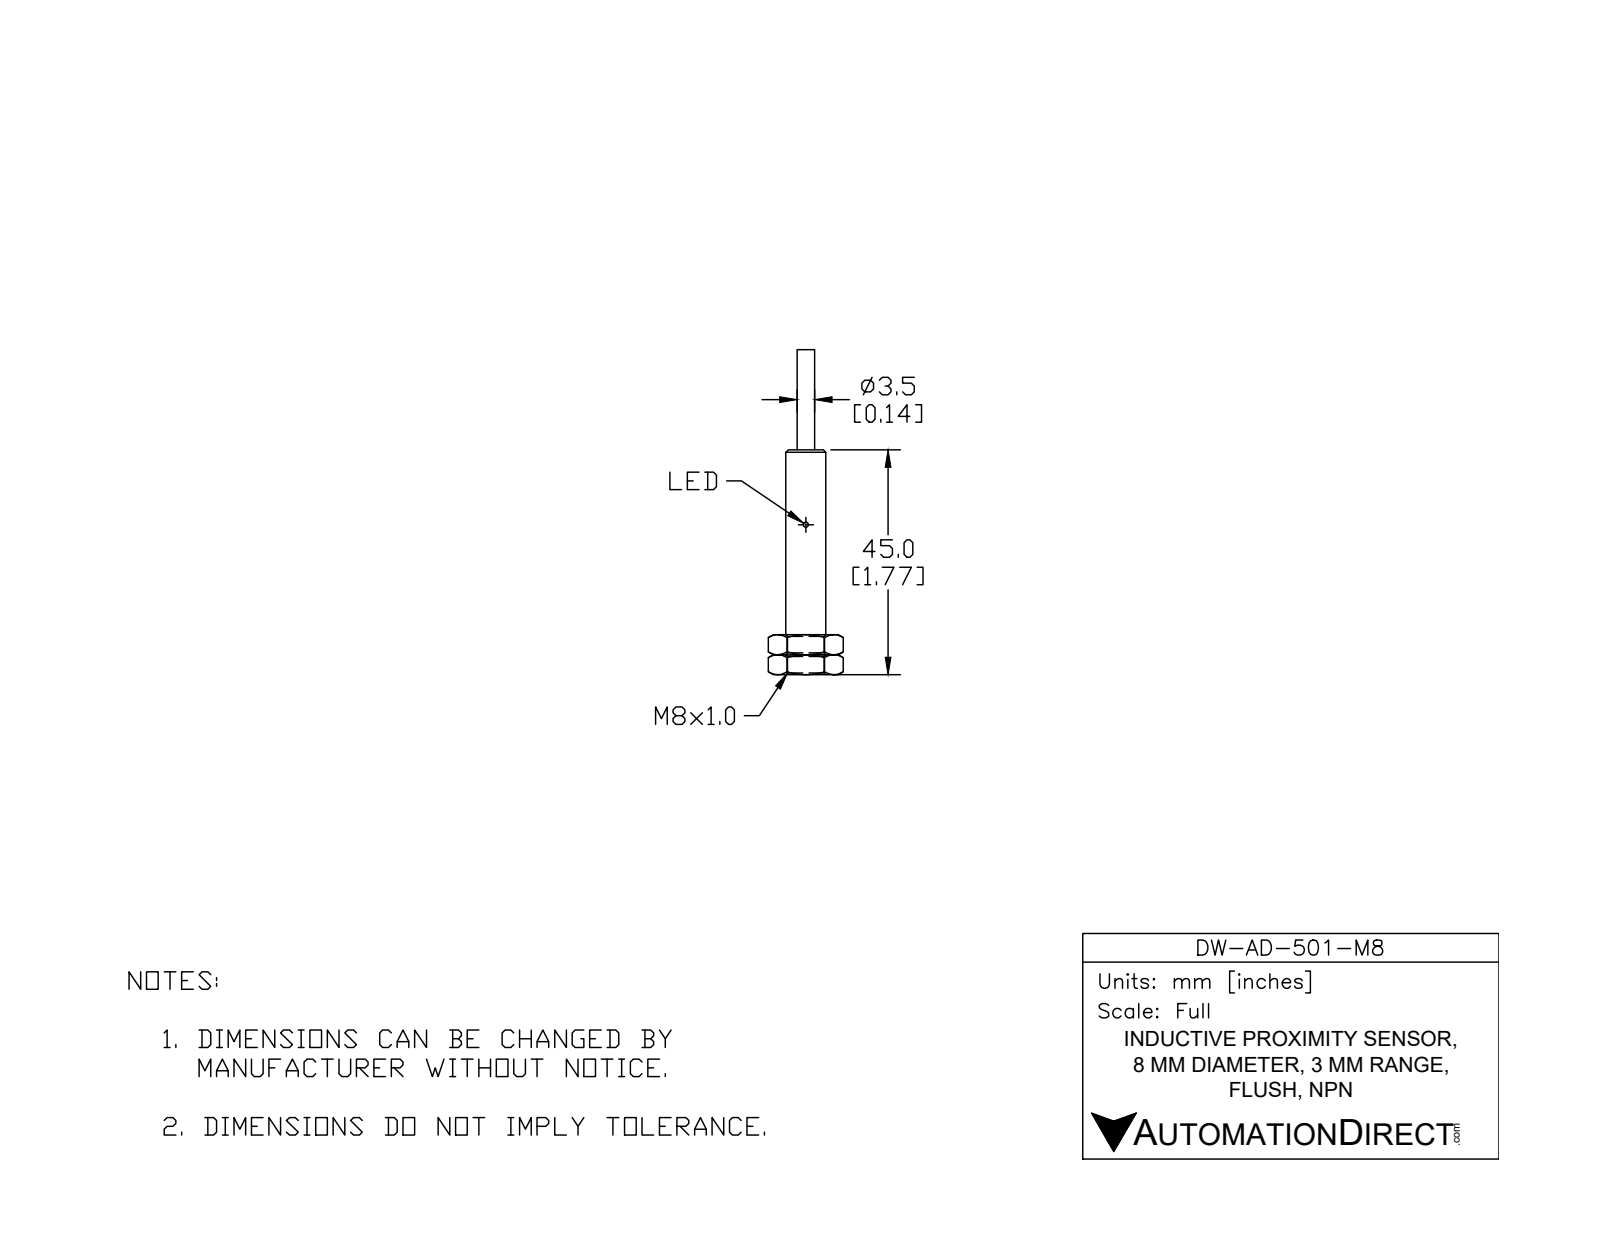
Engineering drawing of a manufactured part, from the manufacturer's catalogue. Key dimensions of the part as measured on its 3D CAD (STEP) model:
Part name (STEP PRODUCT): DW-AD-501-M8
STEP written by: SolidWorks 2017 (AUTOMOTIVE_DESIGN)
Units: inches
Bodies: 1 solid, 10 faces (4 planar, 3 cylindrical, 3 other)
Overall size (bounding box): 2.803 × 0.315 × 0.315
Volume: 0.17 in³ · Surface area: 2.53 in²
Round bosses / shafts (diameter × count): ⌀0.315 ×1, ⌀0.256 ×1, ⌀0.197 ×1
Main face-to-face distances: 2.803, 1.791, 1.012, 1.772, 0.02, 1.031
